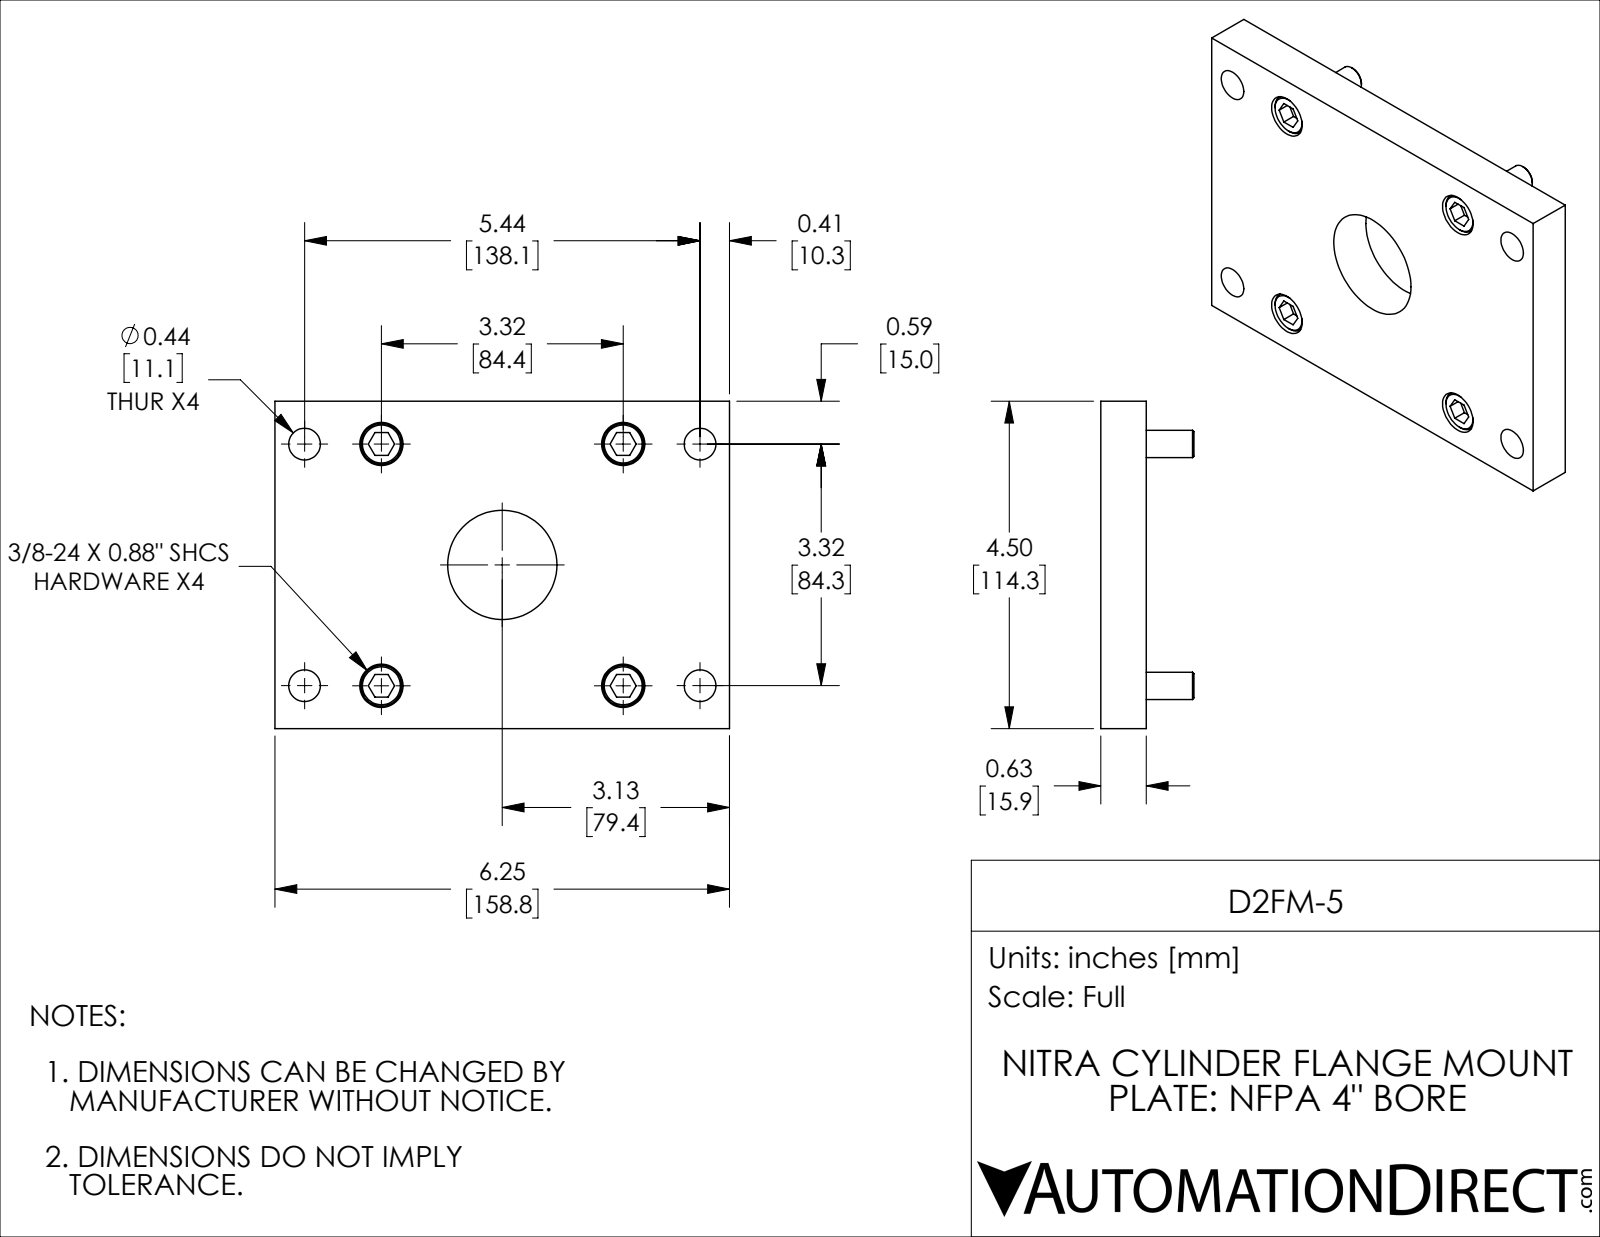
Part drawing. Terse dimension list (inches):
name: D2FM-5
written by: SolidWorks 2019 (CONFIG_CONTROL_DESIGN)
unit: in
bodies: 5 solids, 108 faces (50 planar, 42 cylindrical, 16 other)
size: 6.25 × 4.5 × 1.281
volume: 16.23 in³; area: 83.86 in²
holes: 4× ⌀0.406, 4× ⌀0.437, 4× ⌀0.594, 1× ⌀1.502
bosses: 4× ⌀0.562, 4× ⌀0.375
face distances: 0.625, 4.5, 6.25, 0.219, 0.406, 0.594, 0.375, 0.031, 0.656, 0.875
hole spacings: 1.057, 2.35, 3.185, 3.324, 3.486, 4.381, 5.498, 3.32
